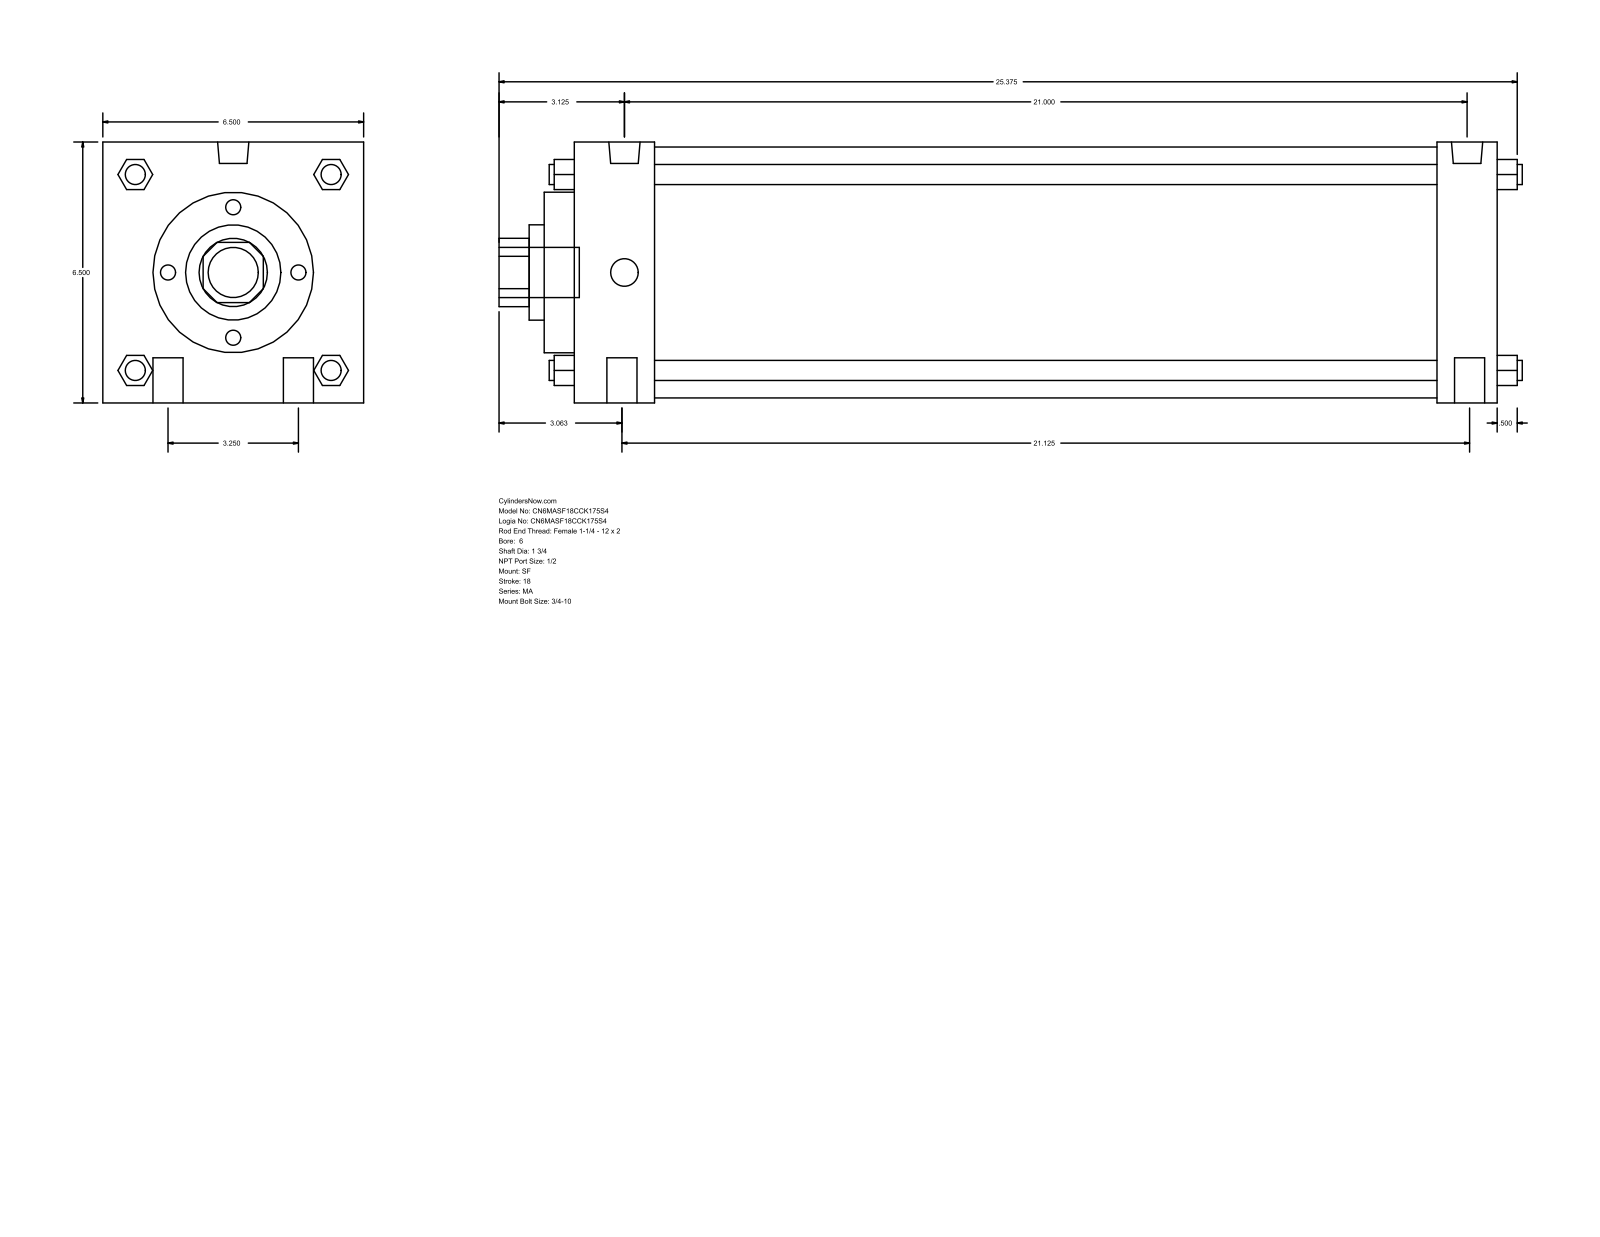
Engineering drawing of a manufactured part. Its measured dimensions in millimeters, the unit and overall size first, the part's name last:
Units: millimetres
Overall size (bounding box): 647.7 × 165.1 × 165.1
Round holes (diameter × count): ⌀44.45 ×1, ⌀60.33 ×1, ⌀101.6 ×1, ⌀158.75 ×1
Round bosses / shafts (diameter × count): ⌀19.05 ×4, ⌀12.7 ×4, ⌀19.77 ×2, ⌀17.46 ×2, ⌀31.75 ×1
Partial cylindrical surfaces — rounded edges, fillets, slot ends (radius × count): R21.63 ×1
Main face-to-face distances: 165.1, 584.21, 19.05, 50.8, 38.1, 546.11, 495.31, 533.41, 69.85, 565.16
Bodies: 0 solids, 126 faces (95 planar, 31 cylindrical, 0 other)
Part name (STEP PRODUCT): MA_SF__0600_1.75
STEP written by: GSSL Pune (CONFIG_CONTROL_DESIGN)
